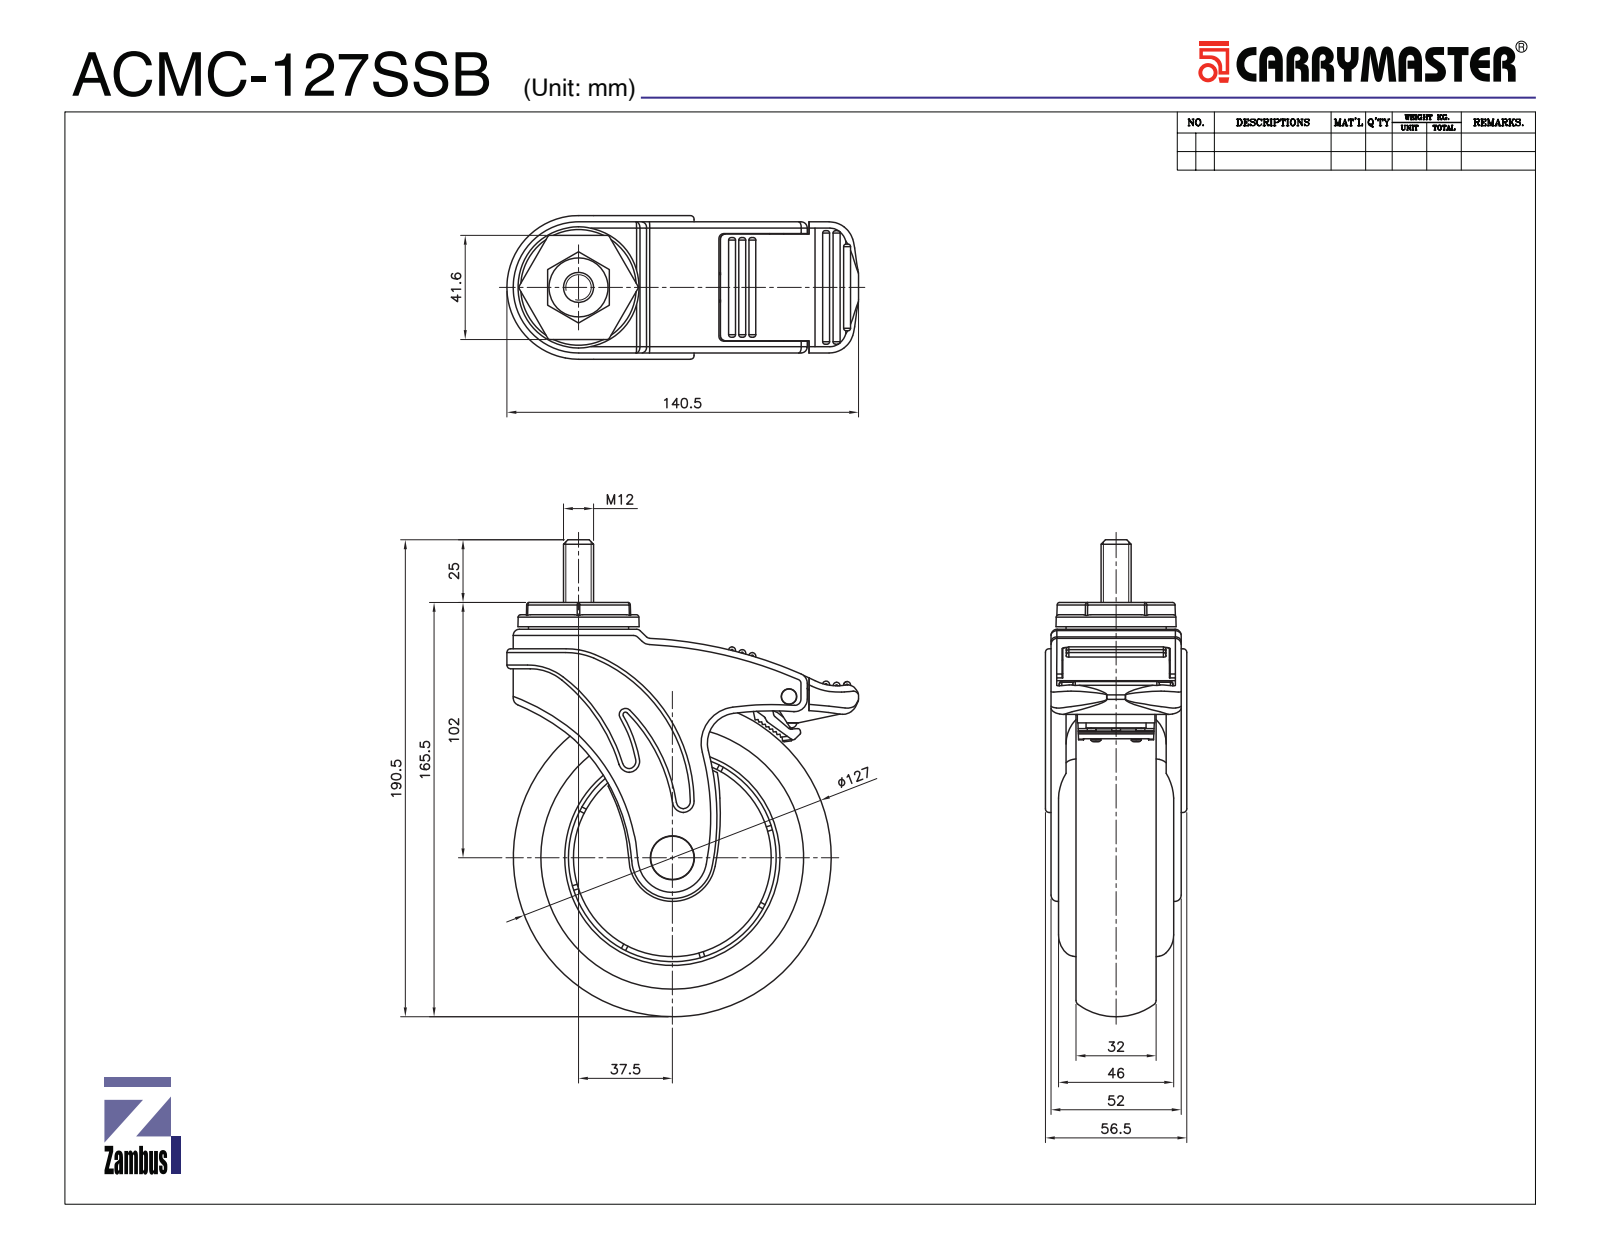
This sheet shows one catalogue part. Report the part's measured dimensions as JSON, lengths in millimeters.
{"part_name": "ACMC-127 WHEEL; ACMC-127 S TOP PLATE; ACMC-127SSB; ACMC-127 BRAKE FRAME (+2 more)", "step_written_by": "SolidWorks 2019 (CONFIG_CONTROL_DESIGN)", "units": "millimeters", "bodies": {"solids": 6, "faces": 635, "planar": 212, "cylindrical": 253, "other": 170}, "overall_size": [190.5, 141.04, 57.1], "volume_mm3": 601226, "surface_area_mm2": 102274, "round_holes": [[17.3, 1], [37, 1], [83, 1], [105.01, 1]], "round_bosses_or_shafts": [[4, 2], [105, 1], [79, 1], [78.59, 1], [40, 1], [22, 1], [17, 1], [10.25, 1]], "partial_cylinders_radius": [[0.5, 27], [1, 16], [2, 8], [1.4, 6], [2.5, 6], [4.5, 4], [1.5, 2], [10, 2]], "face_to_face_distances": [4.25, 36.25, 6, 10.25, 42.25, 46.5, 32, 40.5, 4, 6.25]}
